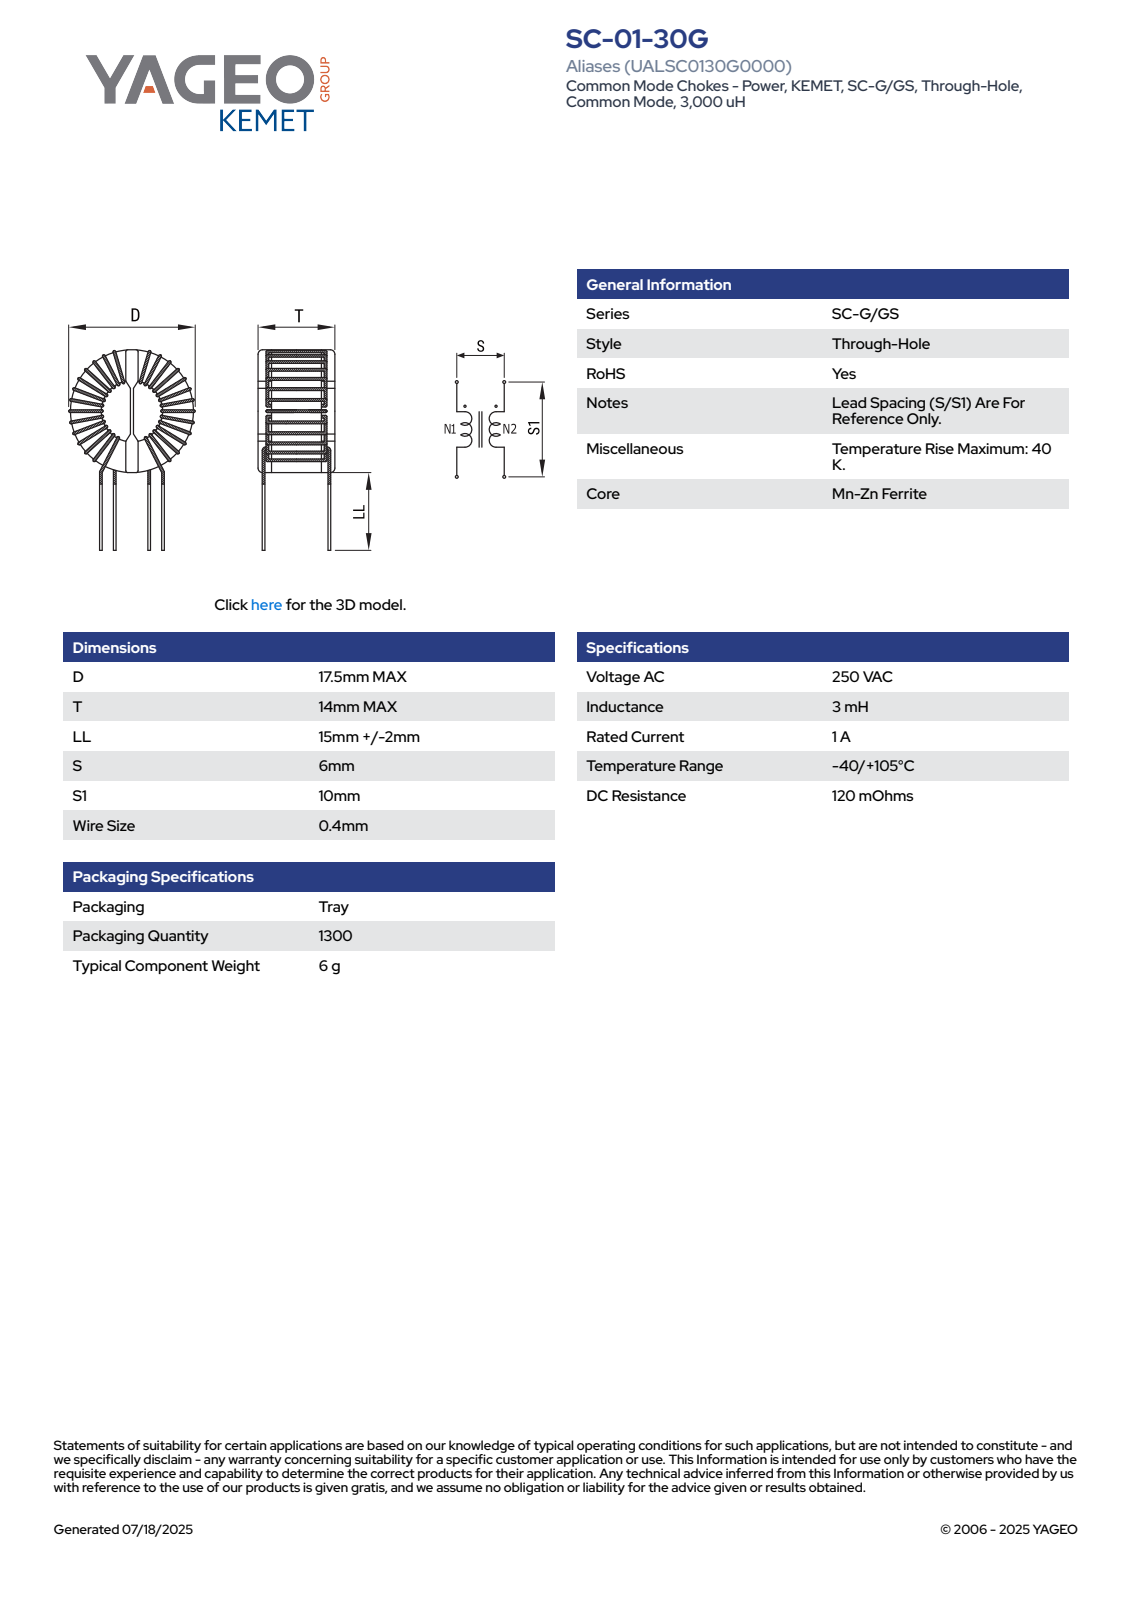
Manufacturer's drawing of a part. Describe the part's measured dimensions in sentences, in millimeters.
The part is named "SC-01-30G". Its 3-D file was written by "SolidWorks 2018 (AUTOMOTIVE_DESIGN)". It is 1 solid with 268 faces: 121 planar, 65 cylindrical and 82 other. Overall it measures 30.37 by 17.5 by 14 millimeters. Its volume is 1 786 cubic millimeters and its surface area 1 710 square millimeters. Round bosses or shafts: 8 of diameter 0.4. Partial cylindrical surfaces (rounded edges, fillets, slot ends): 16 of radius 0.2, 1 of radius 2.32, 1 of radius 3.21, 1 of radius 3.62, 1 of radius 3.67, 1 of radius 3.8, 1 of radius 6.35, 1 of radius 6.4. The main face-to-face distances are 1.2, 2, 8.3, 0.8, 3.2, 2.85, 11.15, 1.15, 2.05, 0.85.
